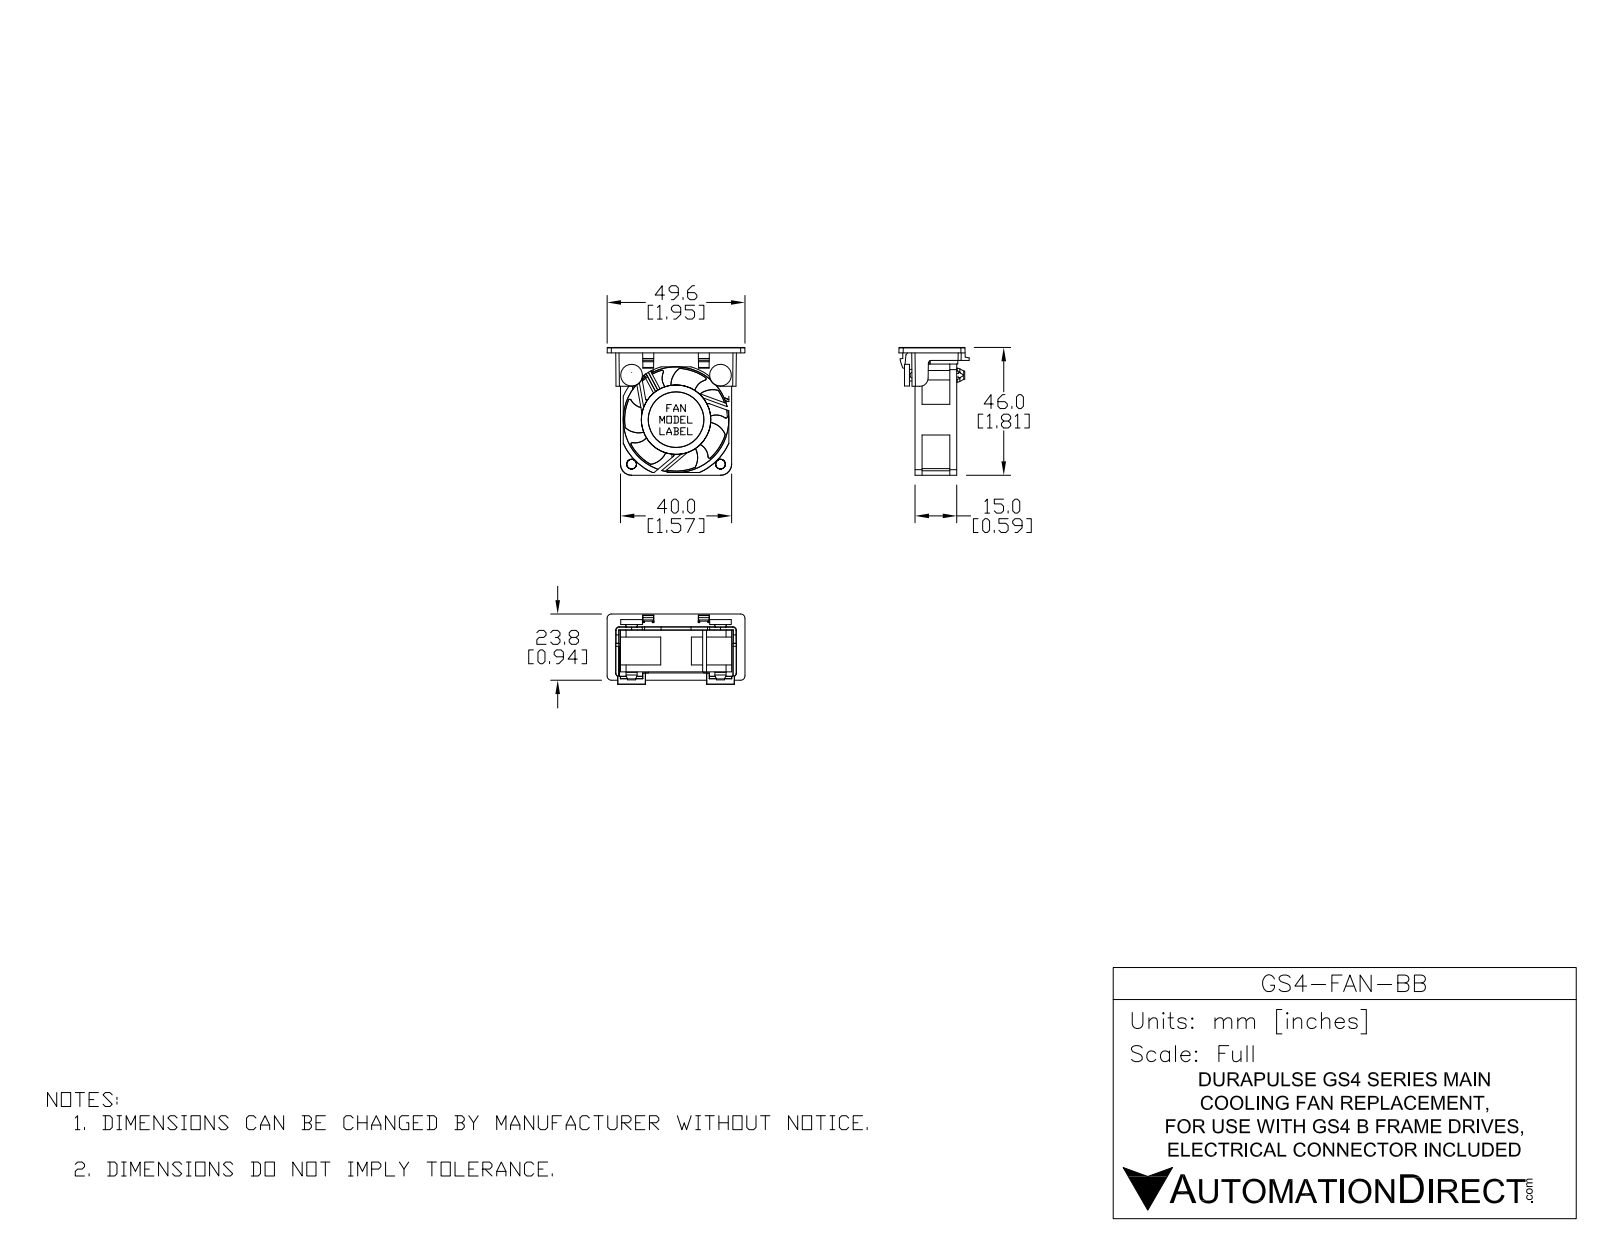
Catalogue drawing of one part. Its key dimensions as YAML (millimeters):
part_name: "GS4-FAN-BB"
step_written_by: "SolidWorks 2016 (AUTOMOTIVE_DESIGN)"
units: millimeters
bodies: {solids: 3, faces: 301, planar: 187, cylindrical: 75, other: 39}
overall_size: [51.1, 46, 29]
volume: 11900
surface_area: 14670
round_holes:
  - {diameter: 3.5, count: 6}
  - {diameter: 4.2, count: 1}
round_bosses_or_shafts:
  - {diameter: 18, count: 1}
partial_cylinders:
  - {radius: 0.2, count: 16}
  - {radius: 1, count: 5}
  - {radius: 1.5, count: 4}
  - {radius: 2, count: 4}
  - {radius: 1.2, count: 2}
  - {radius: 2, count: 2}
  - {radius: 3, count: 1}
face_to_face_distances: [0.5, 15, 2.5, 2, 39, 4, 6, 3.5, 1, 2.7]
hole_center_spacings: [32, 45.3]
